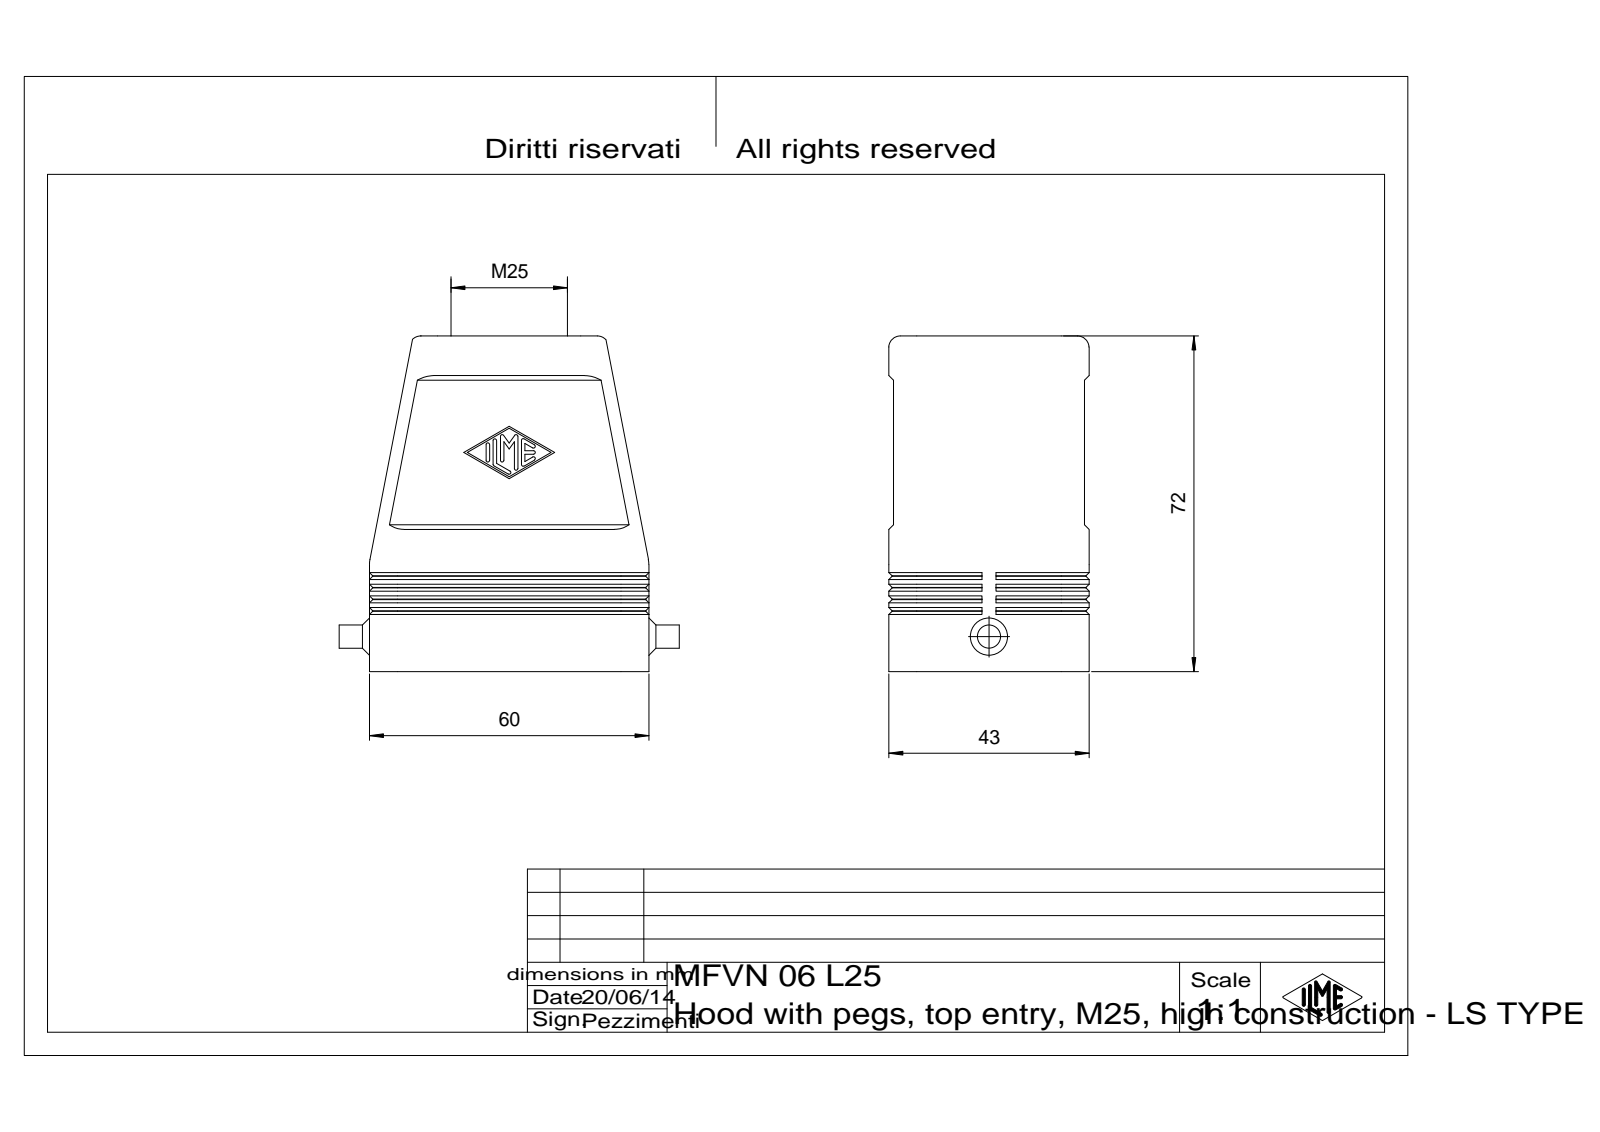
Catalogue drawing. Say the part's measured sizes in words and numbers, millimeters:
The part is named "MFVN_06_L25". Its 3-D file was written by "CoCreate Modeling 16.00A 16-Aug-2008 (C) Parametric Technology GmbH (AUTOMOTIVE_DESIGN)". It is 1 solid with 302 faces: 140 planar, 110 cylindrical and 52 other. Overall it measures 73 by 72 by 43 millimeters. Its volume is 53 101 cubic millimeters and its surface area 28 357 square millimeters. Round holes: 4 of diameter 2.46, 4 of diameter 4, 1 of diameter 25. Round bosses or shafts: 1 of diameter 5. Partial cylindrical surfaces (rounded edges, fillets, slot ends): 10 of radius 6, 4 of radius 2, 4 of radius 2.5, 4 of radius 3, 4 of radius 5.3. The main face-to-face distances are 4, 38, 3, 1, 39, 42, 35, 7, 11, 41. The hole center spacings are 25.81, 27, 44, 51.62.
